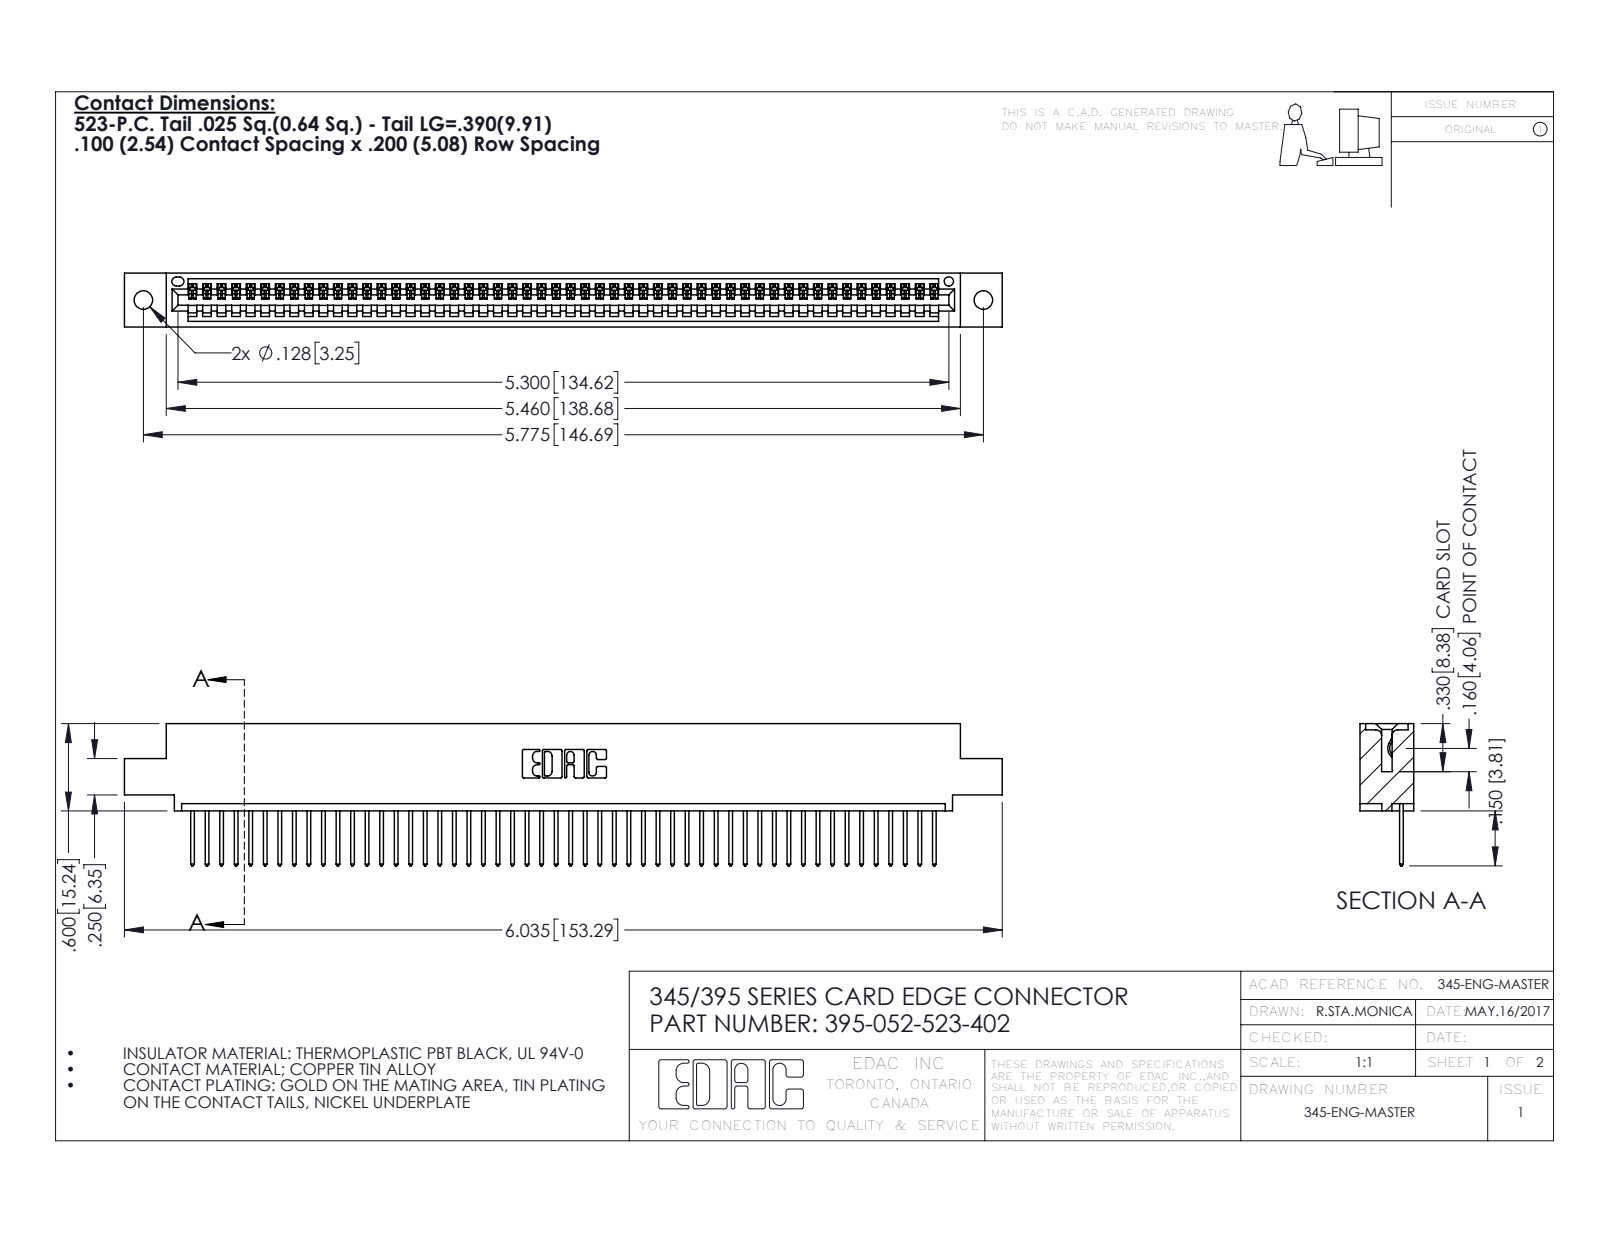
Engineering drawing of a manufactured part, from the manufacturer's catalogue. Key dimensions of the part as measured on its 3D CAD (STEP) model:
Part name (STEP PRODUCT): 345 Part_0.110 Offset - 0.128 Dia; 345-292-001_345-293-123; 395-052-523-402
STEP written by: SolidWorks 2016 (CONFIG_CONTROL_DESIGN)
Units: inches
Bodies: 53 solids, 3146 faces (2164 planar, 982 cylindrical, 0 other)
Overall size (bounding box): 6.035 × 0.977 × 0.37
Volume: 0.886 in³ · Surface area: 29.9 in²
Round holes (diameter × count): ⌀0.128 ×2, ⌀0.064 ×1
Partial cylindrical surfaces — rounded edges, fillets, slot ends (radius × count): R0.006 ×104, R0.01 ×104, R0.01 ×22, R0.007 ×6, R0.031 ×6, R0.026 ×3, R0.031 ×2, R0.04 ×2
Main face-to-face distances: 0.298, 0.072, 0.37, 0.098, 0.272, 0.025, 0.2, 0.225, 0.149, 0.072
Hole centre spacings: 0.27, 5.539, 5.775
